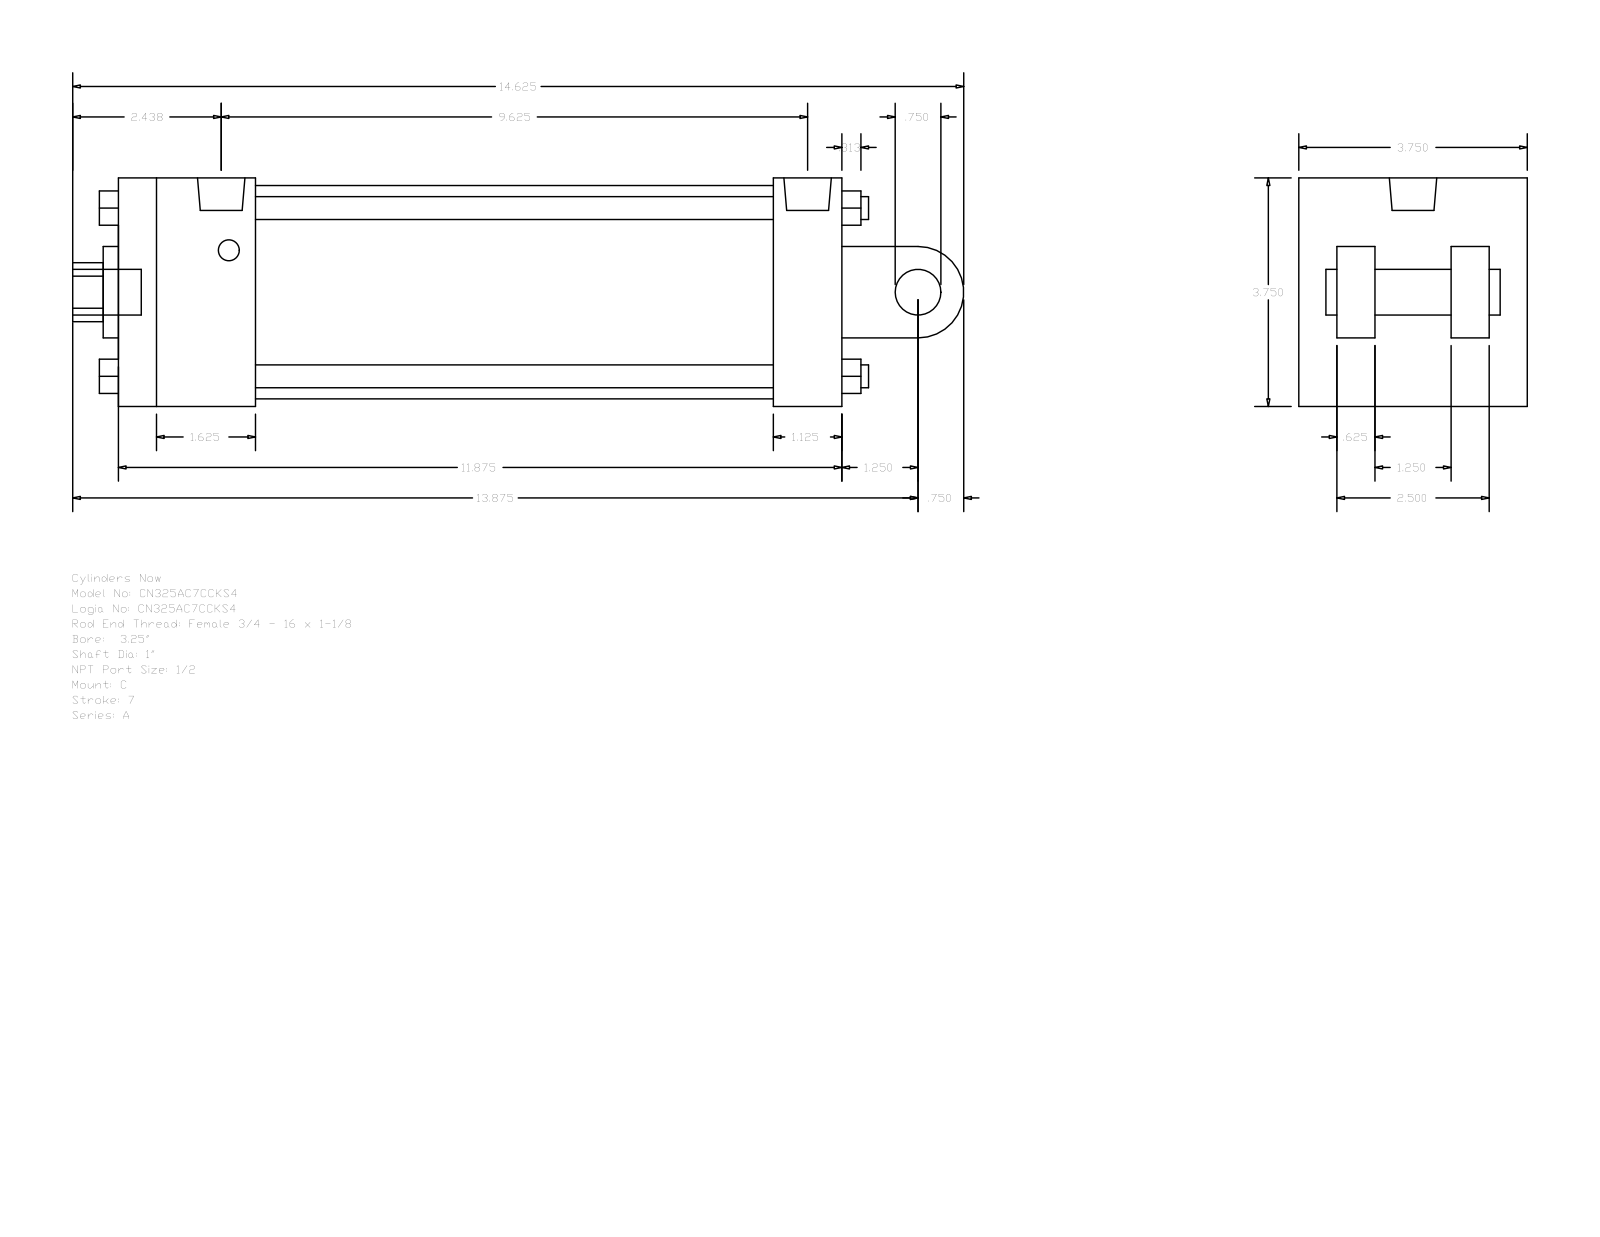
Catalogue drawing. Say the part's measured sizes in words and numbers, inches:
The part is named "A_C__0325_1". Its 3-D file was written by "GSSL Pune (CONFIG_CONTROL_DESIGN)". It is 0 solids with 135 faces: 102 planar, 33 cylindrical and 0 other. Overall it measures 14.625 by 3.75 by 3.75 inches. Round holes: 2 of diameter 0.344, 1 of diameter 0.778, 1 of diameter 1, 1 of diameter 1.5, 1 of diameter 3.5. Round bosses or shafts: 4 of diameter 0.375, 2 of diameter 0.75, 2 of diameter 0.344, 1 of diameter 0.778. Partial cylindrical surfaces (rounded edges, fillets, slot ends): 1 of radius 0.484, 1 of radius 0.75. The main face-to-face distances are 3.75, 11.875, 0.625, 2.5, 1.875, 3.125, 1.25, 2.625, 10.75, 1.125. The hole center spacings are 0.125.
